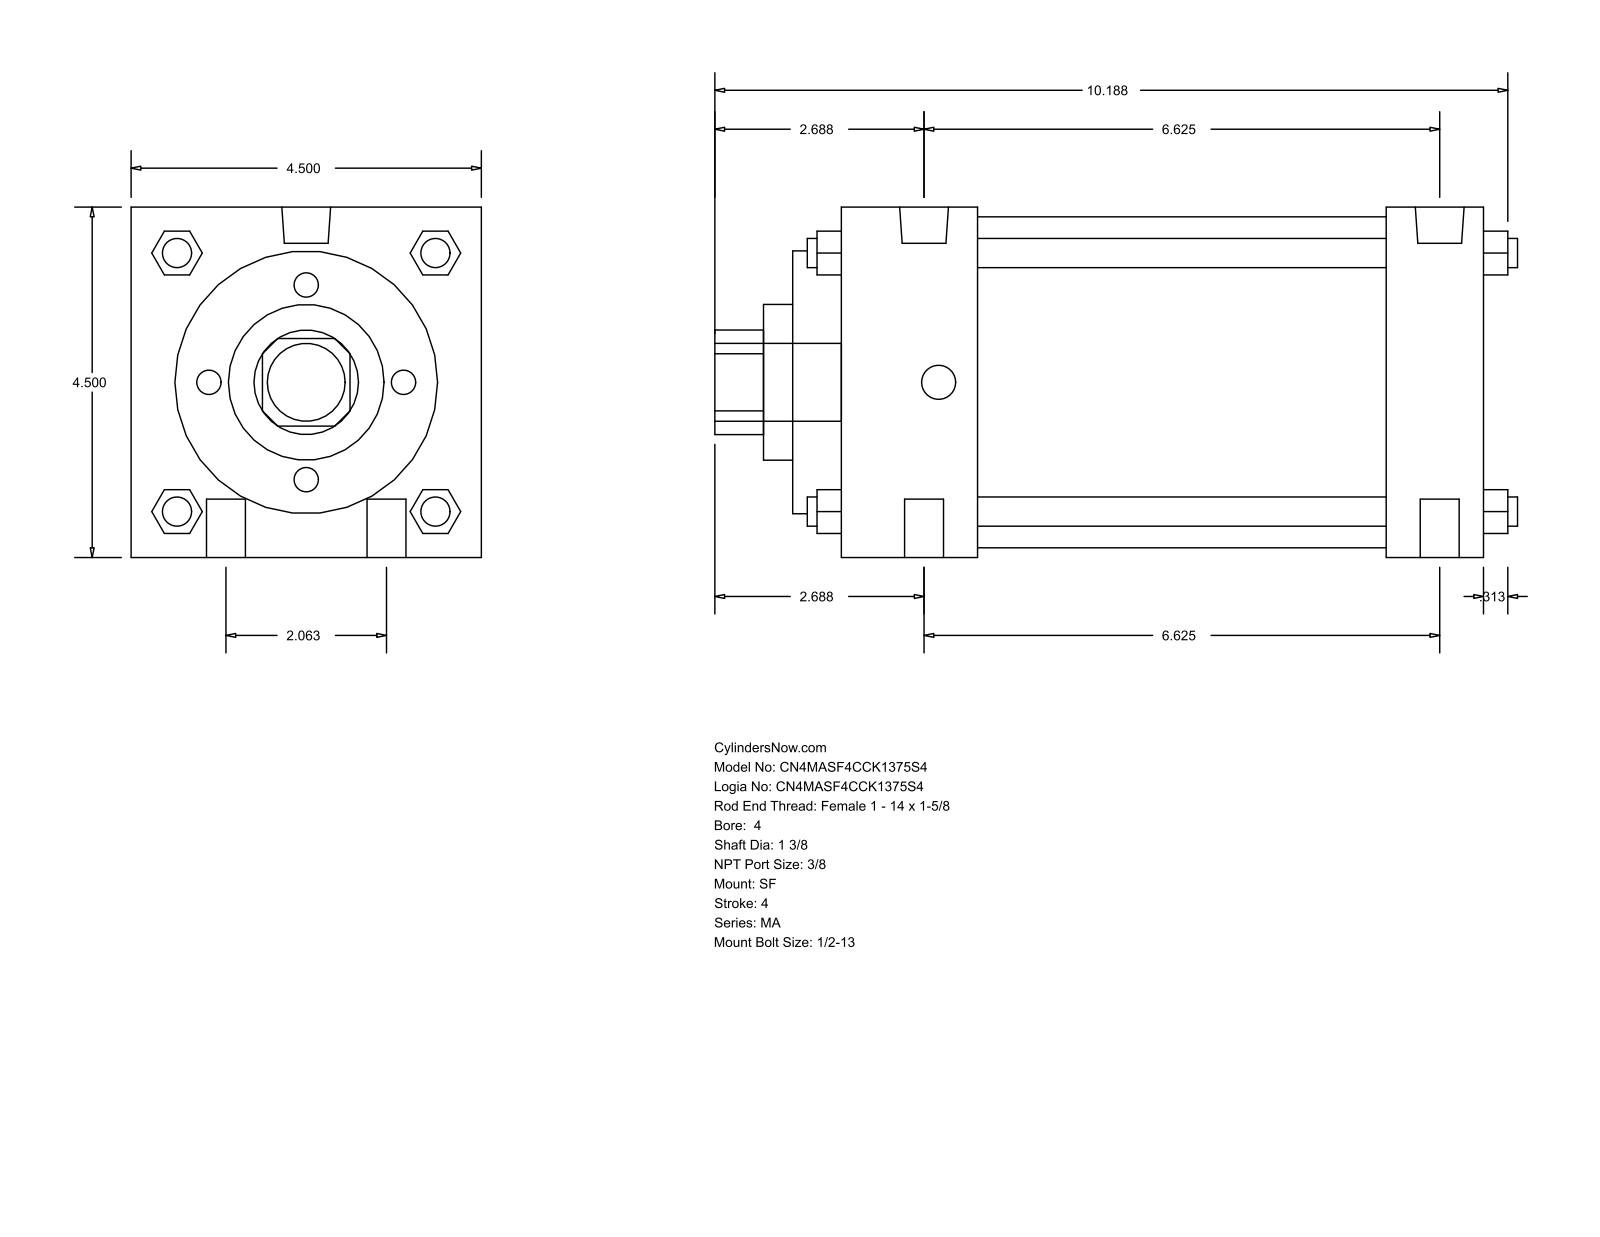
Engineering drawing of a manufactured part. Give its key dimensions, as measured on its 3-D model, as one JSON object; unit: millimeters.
{"part_name": "MA_SF__0400_1.375", "step_written_by": "GSSL Pune (CONFIG_CONTROL_DESIGN)", "units": "millimeters", "bodies": {"solids": 0, "faces": 126, "planar": 95, "cylindrical": 31, "other": 0}, "overall_size": [261.94, 114.3, 114.3], "round_holes": [[34.92, 1], [50.8, 1], [85.72, 1], [107.95, 1]], "round_bosses_or_shafts": [[12.7, 4], [9.53, 4], [15.93, 2], [11.11, 2], [25.4, 1]], "partial_cylinders_radius": [[17.06, 1]], "face_to_face_distances": [114.3, 209.55, 225.42, 15.87, 193.67, 177.8, 31.75, 60.32, 44.45, 133.35]}
